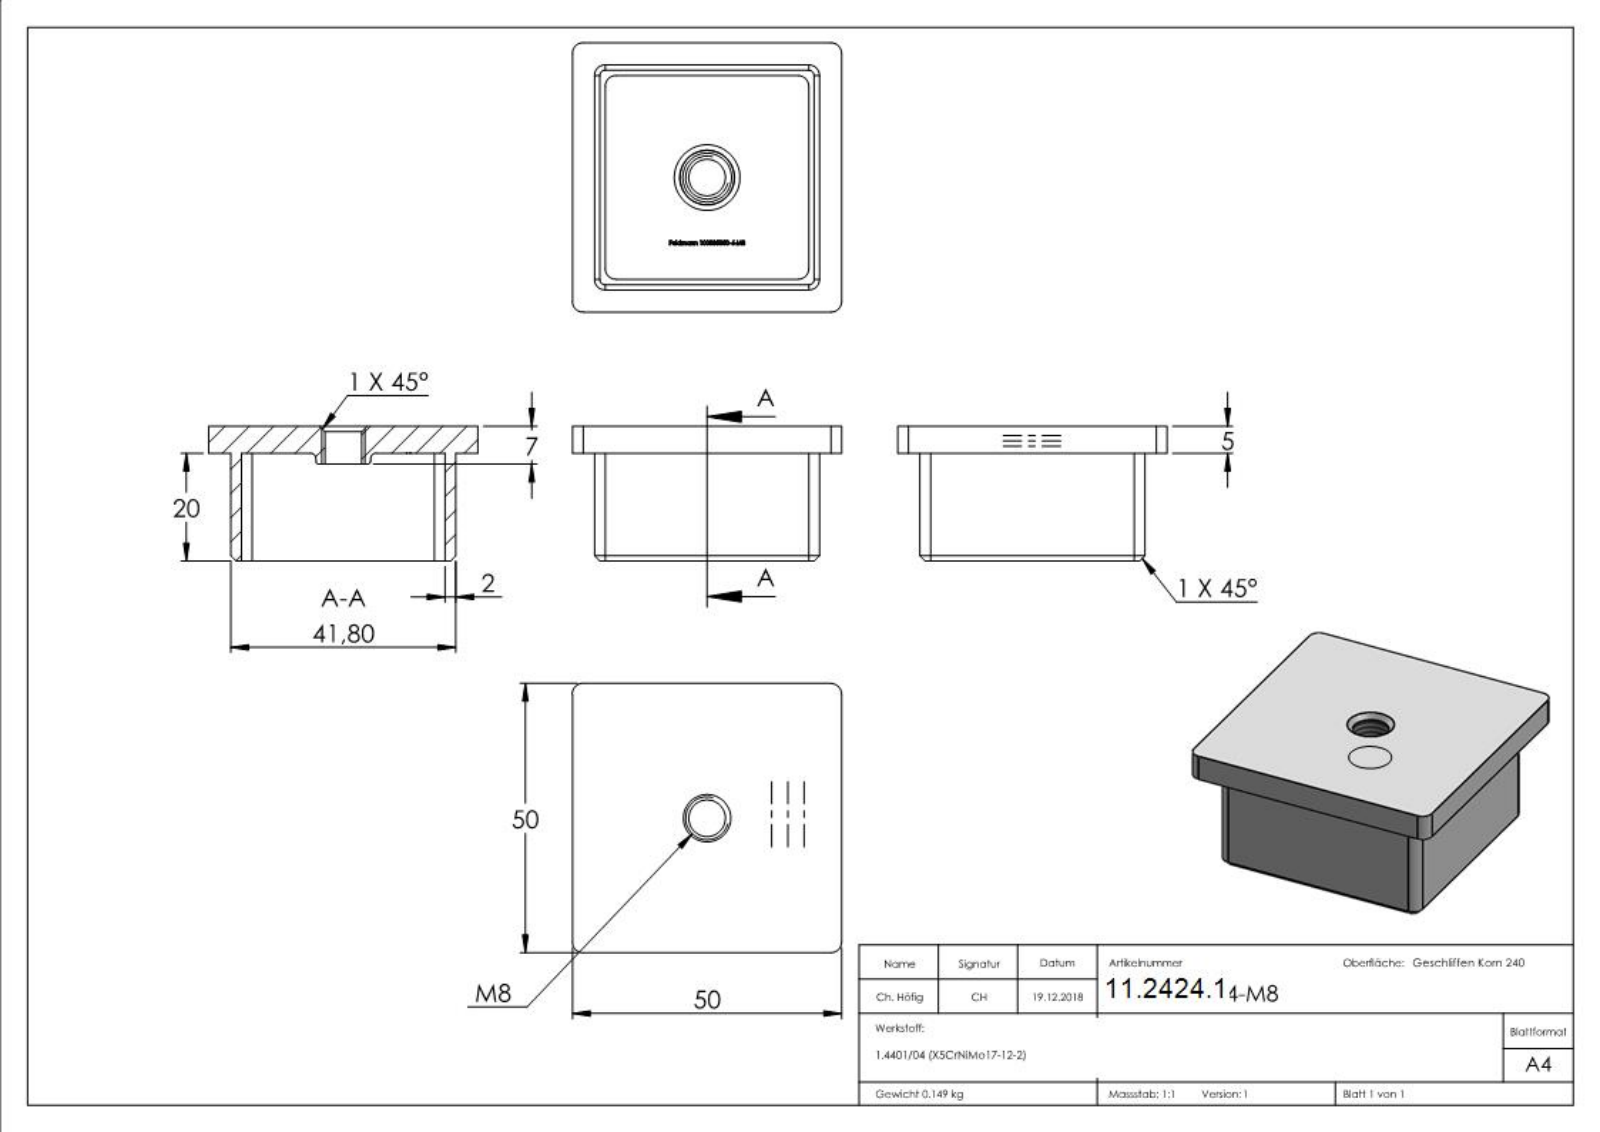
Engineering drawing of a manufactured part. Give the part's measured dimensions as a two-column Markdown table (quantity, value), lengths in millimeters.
| quantity | value |
| --- | --- |
| part name | 100035050-4-M8 |
| STEP written by | SolidWorks 2015 (CONFIG_CONTROL_DESIGN) |
| units | millimeters |
| bodies | 1 solid, 329 faces (163 planar, 14 cylindrical, 152 other) |
| overall size | 50 × 50 × 25 |
| volume | 18 671 mm³ |
| surface area | 12 225 mm² |
| round holes (diameter × count) | 6.8 × 1 |
| partial cylindrical surfaces (radius × count) | 2 × 12 |
| main face-to-face distances | 2, 39.8, 5, 41.8, 37.8, 4.1, 6.1, 43.9, 45.9, 50 |
